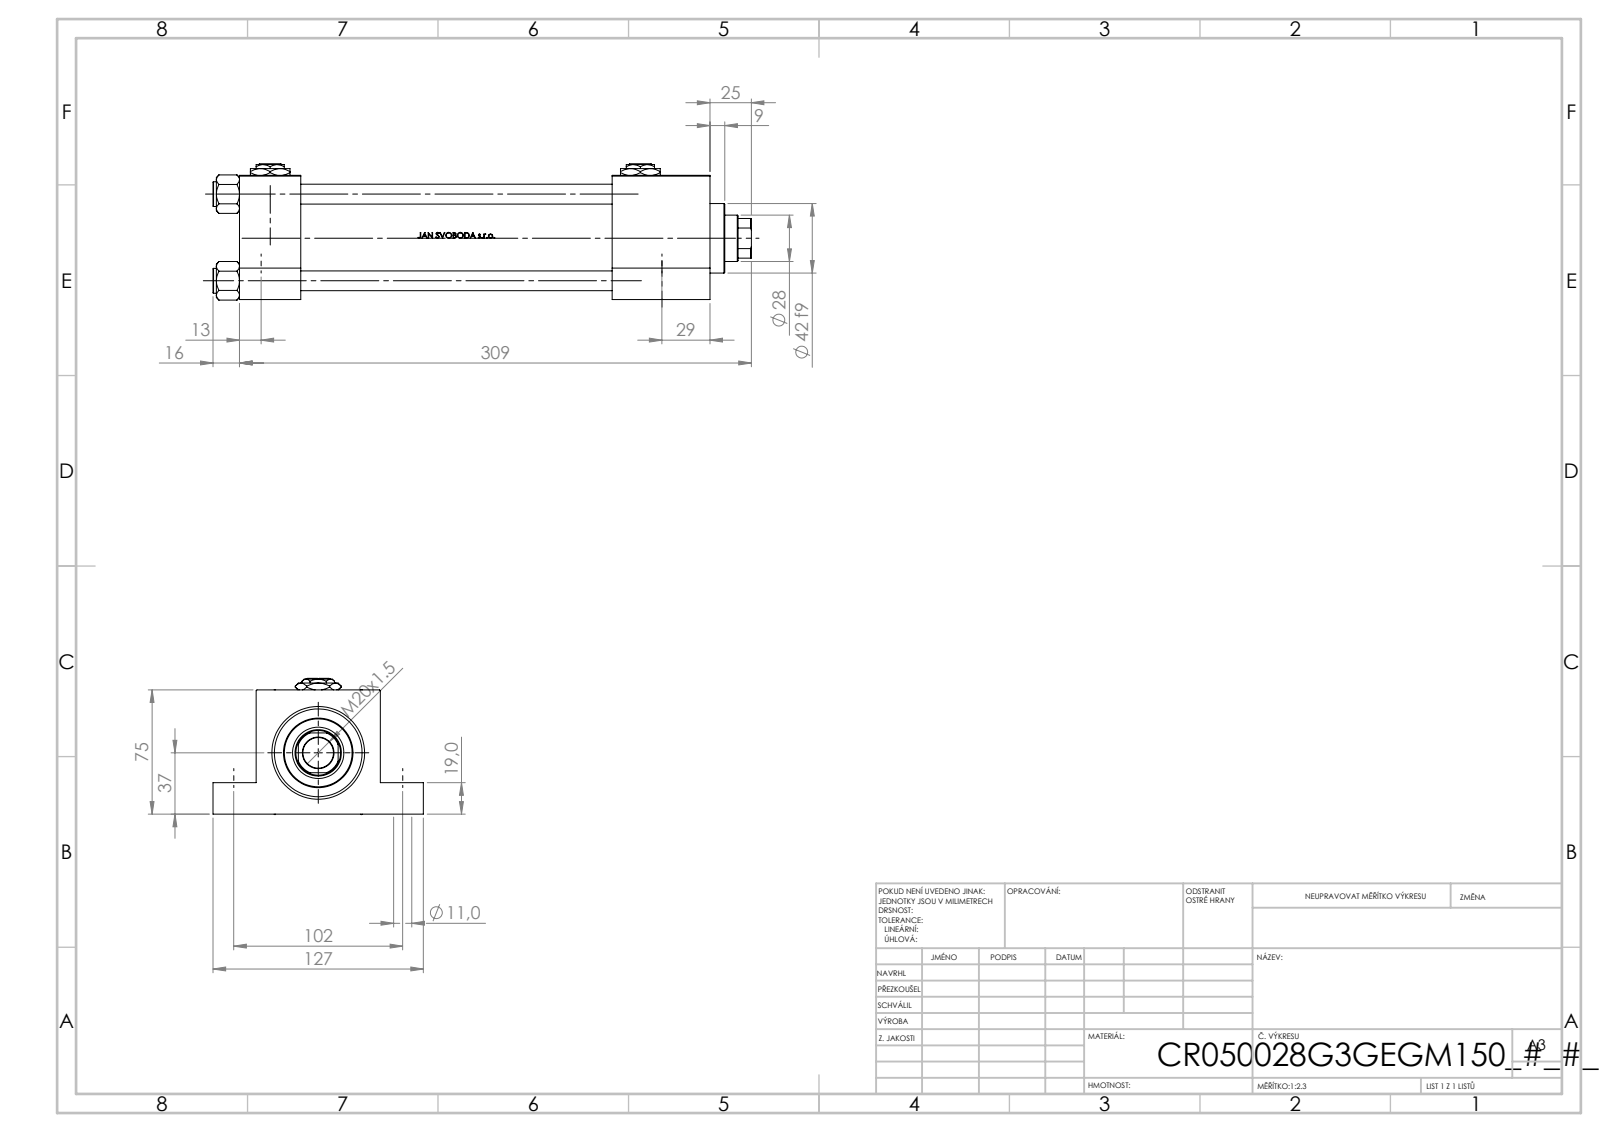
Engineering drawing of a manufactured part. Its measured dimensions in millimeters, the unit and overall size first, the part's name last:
Units: millimetres
Overall size (bounding box): 325 × 127 × 82.27
Round holes (diameter × count): ⌀12 ×4, ⌀14 ×4, ⌀7 ×2, ⌀20.96 ×2, ⌀30 ×2, ⌀18.5 ×1, ⌀28 ×1, ⌀31 ×1, ⌀41 ×1, ⌀50 ×1, ⌀53 ×1
Round bosses / shafts (diameter × count): ⌀15 ×4, ⌀56 ×1, ⌀42 ×1
Partial cylindrical surfaces — rounded edges, fillets, slot ends (radius × count): R13.5 ×1
Main face-to-face distances: 75, 37, 284, 247, 56, 19, 225, 188, 59, 26
Hole centre spacings: 36.98, 52.3, 51.3, 52.63, 73.96, 102, 234.61, 241.94
Volume: 1 037 000 mm³ · Surface area: 264 154 mm²
Bodies: 17 solids, 1252 faces (496 planar, 136 cylindrical, 620 other)
Part name (STEP PRODUCT): NUT_M5_G; V215CR_G_Body; Zatka_pro_OIL_PORT; V215CR_VCP_G (+2 more)
STEP written by: SolidWorks 2019 (CONFIG_CONTROL_DESIGN)
